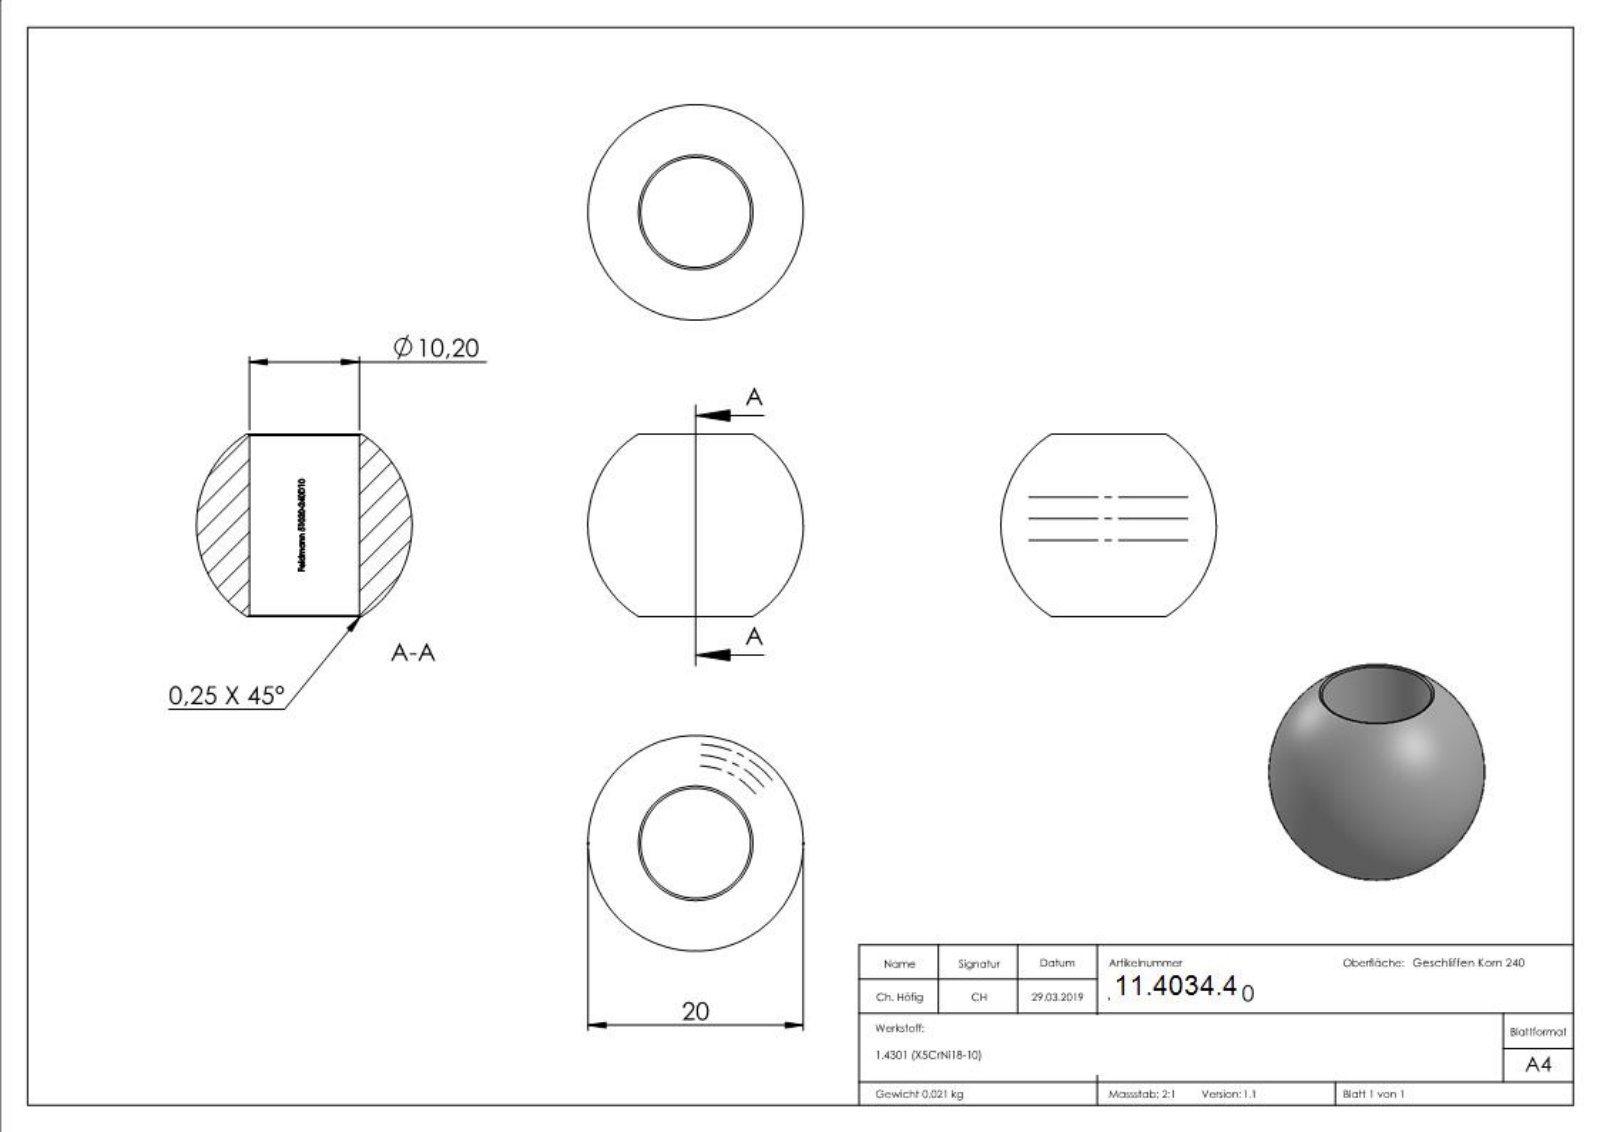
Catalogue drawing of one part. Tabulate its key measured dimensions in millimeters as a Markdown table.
| quantity | value |
| --- | --- |
| part name | 51020-240D10 |
| STEP written by | SolidWorks 2015 (CONFIG_CONTROL_DESIGN) |
| units | millimeters |
| bodies | 1 solid, 255 faces (107 planar, 31 cylindrical, 117 other) |
| overall size | 20 × 20 × 16.95 |
| volume | 2 664 mm³ |
| surface area | 1 620 mm² |
| round holes (diameter × count) | 10.2 × 1 |
| partial cylindrical surfaces (radius × count) | 5.2 × 1 |
| main face-to-face distances | 0.66, 0.61, 6.46, 2.98, 5.85, 1.27, 0.35, 3.48, 7.12, 3.64 |
